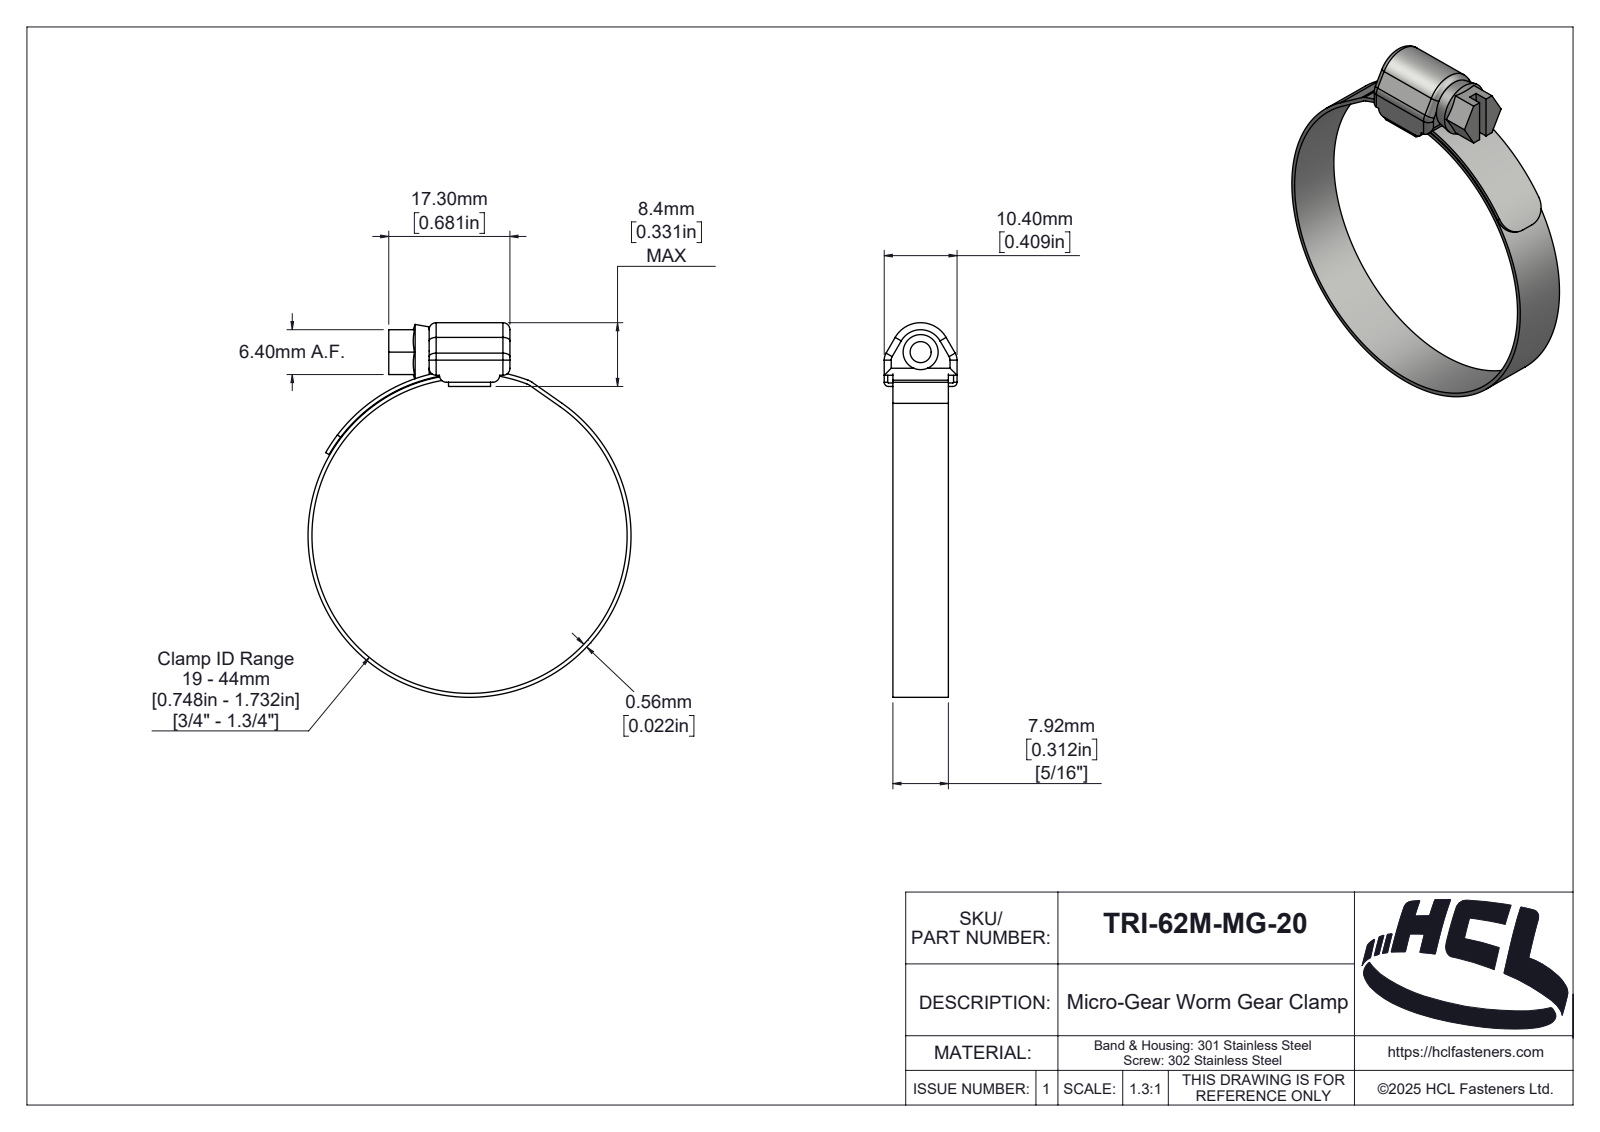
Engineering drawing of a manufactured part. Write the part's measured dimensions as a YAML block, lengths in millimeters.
part_name: "TRI-62M-MG-20"
step_written_by: "SolidWorks 2025 (AUTOMOTIVE_DESIGN)"
units: millimeters
bodies: {solids: 3, faces: 186, planar: 38, cylindrical: 87, other: 61}
overall_size: [53.46, 46.12, 10.4]
volume: 1686
surface_area: 4015
round_holes:
  - {diameter: 5, count: 1}
  - {diameter: 45, count: 1}
round_bosses_or_shafts:
  - {diameter: 46.12, count: 1}
partial_cylinders:
  - {radius: 1, count: 12}
  - {radius: 2, count: 3}
  - {radius: 0.1, count: 2}
  - {radius: 0.6, count: 2}
  - {radius: 3, count: 2}
  - {radius: 0.25, count: 1}
  - {radius: 1.01, count: 1}
  - {radius: 1.26, count: 1}
face_to_face_distances: [7.92, 1.1, 0.5, 1.24, 9.16, 1.6, 0.56, 6.2, 10.4, 5.76]
